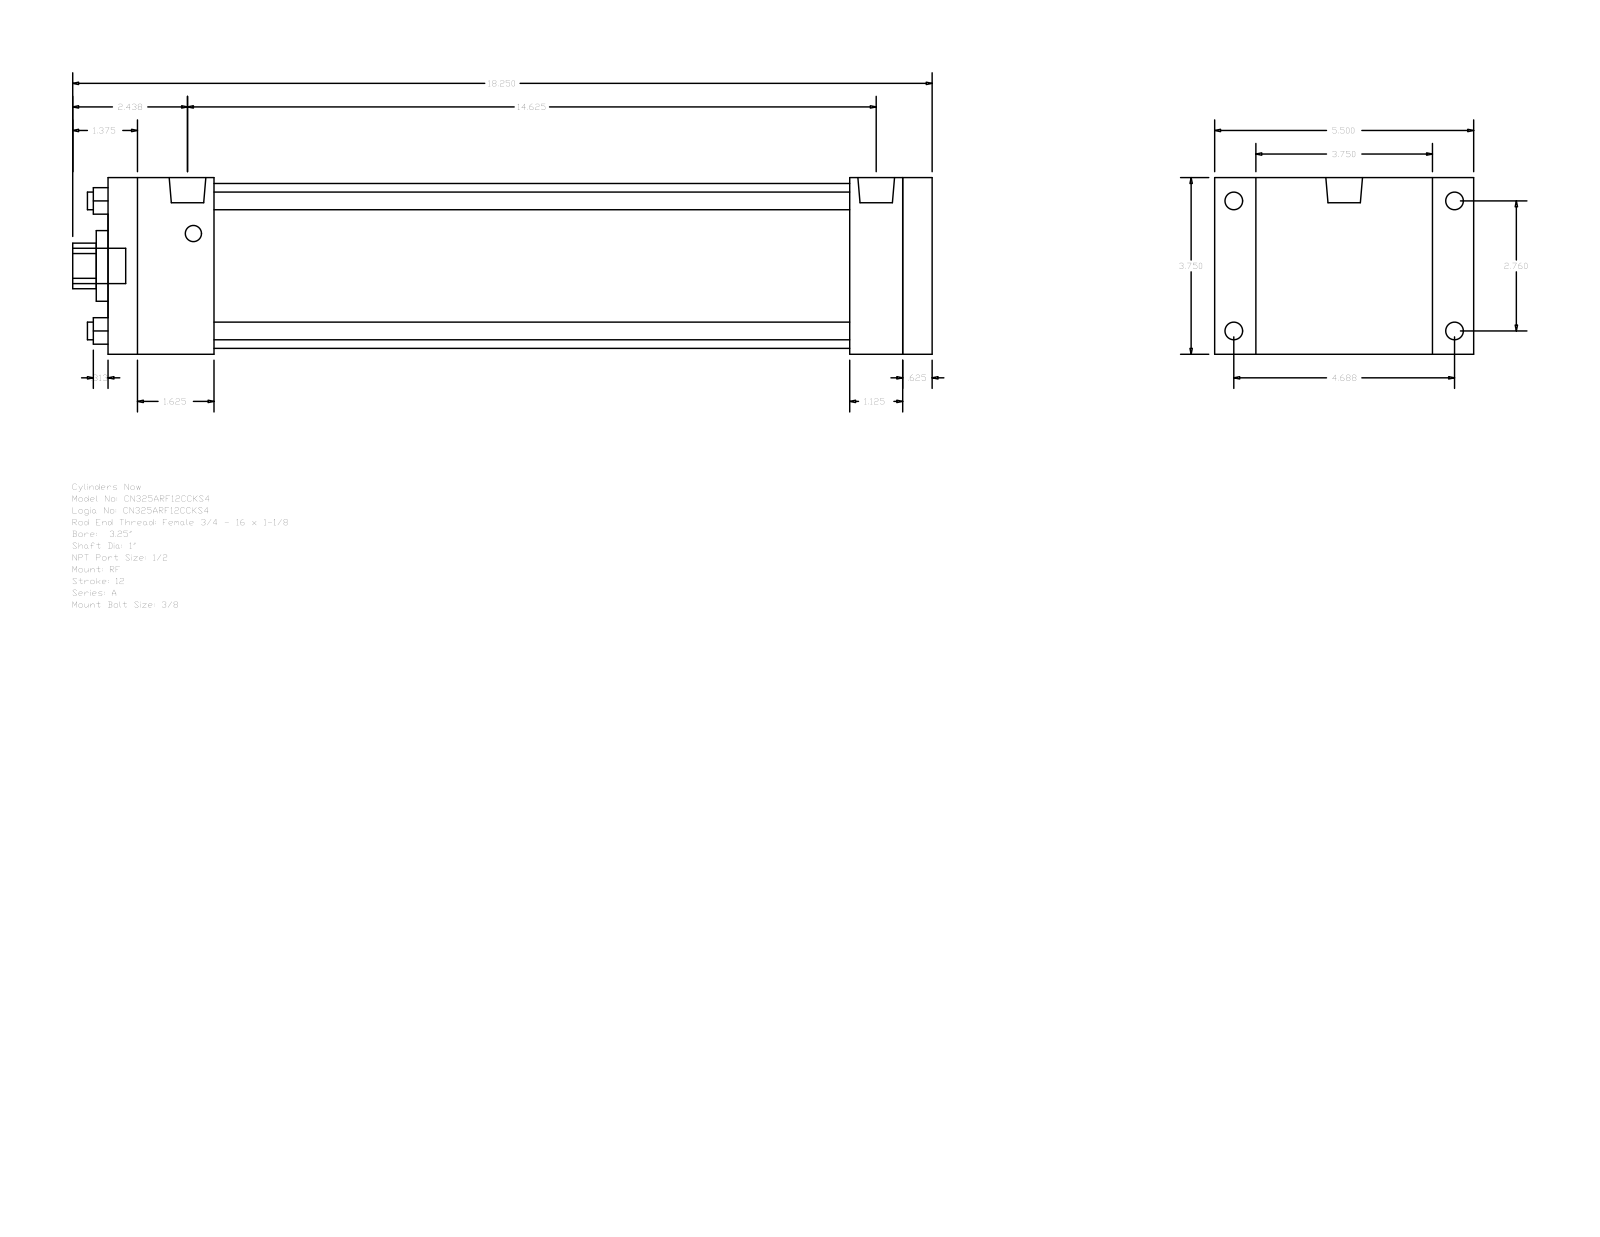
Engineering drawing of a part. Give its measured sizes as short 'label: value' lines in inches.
name: A_RF__0325_1
written by: GSSL Pune (CONFIG_CONTROL_DESIGN)
unit: in
bodies: 0 solids, 92 faces (64 planar, 28 cylindrical, 0 other)
size: 18.25 × 5.5 × 3.75
holes: 4× ⌀0.375, 1× ⌀1, 1× ⌀1.5, 1× ⌀3.5
bosses: 4× ⌀0.375, 4× ⌀0.344, 2× ⌀0.778, 1× ⌀0.75
rounds: 1× R0.484
face distances: 3.75, 17.5, 0.625, 16.875, 0.875, 4.625, 15.75, 1.125, 1.75, 2.25
hole spacings: 1.952, 2.76, 3.903
